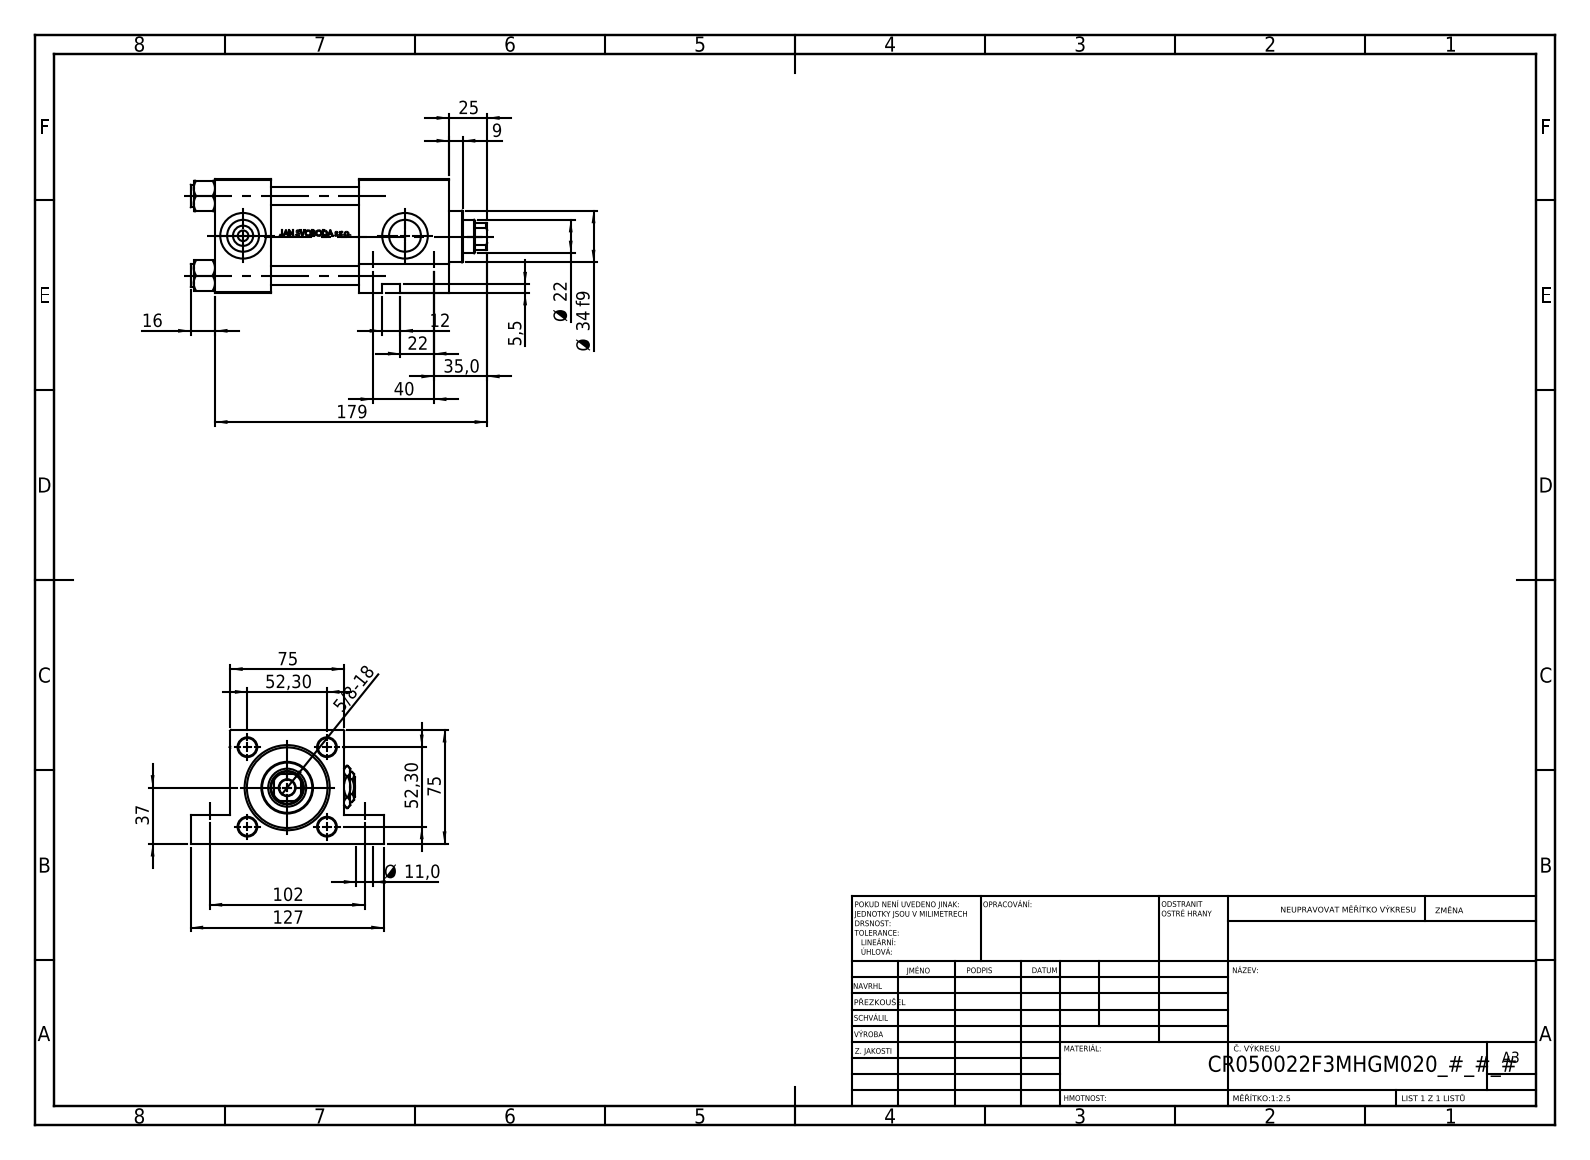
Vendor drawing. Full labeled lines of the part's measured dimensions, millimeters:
Part name (STEP PRODUCT): V215_VC_A; V215CR_F_Body; V215CR_F_TYCINKA; V215CR_VCP_F (+2 more)
STEP written by: SolidWorks 2019 (CONFIG_CONTROL_DESIGN)
Units: millimetres
Bodies: 13 solids, 1199 faces (483 planar, 134 cylindrical, 582 other)
Overall size (bounding box): 195 × 127 × 75
Volume: 702 130 mm³ · Surface area: 160 606 mm²
Round holes (diameter × count): ⌀12 ×4, ⌀20.96 ×3, ⌀30 ×3, ⌀7 ×2, ⌀11 ×2, ⌀11 ×2, ⌀10.5 ×1, ⌀17 ×1, ⌀22 ×1, ⌀25 ×1, ⌀41 ×1, ⌀50 ×1
Round bosses / shafts (diameter × count): ⌀15 ×4, ⌀56 ×1, ⌀34 ×1
Partial cylindrical surfaces — rounded edges, fillets, slot ends (radius × count): R10.5 ×1
Main face-to-face distances: 75, 37, 154, 117, 95, 58, 59, 19, 56, 125.3
Hole centre spacings: 52.3, 36.63, 37.34, 40, 73.96, 102, 109.56, 13
